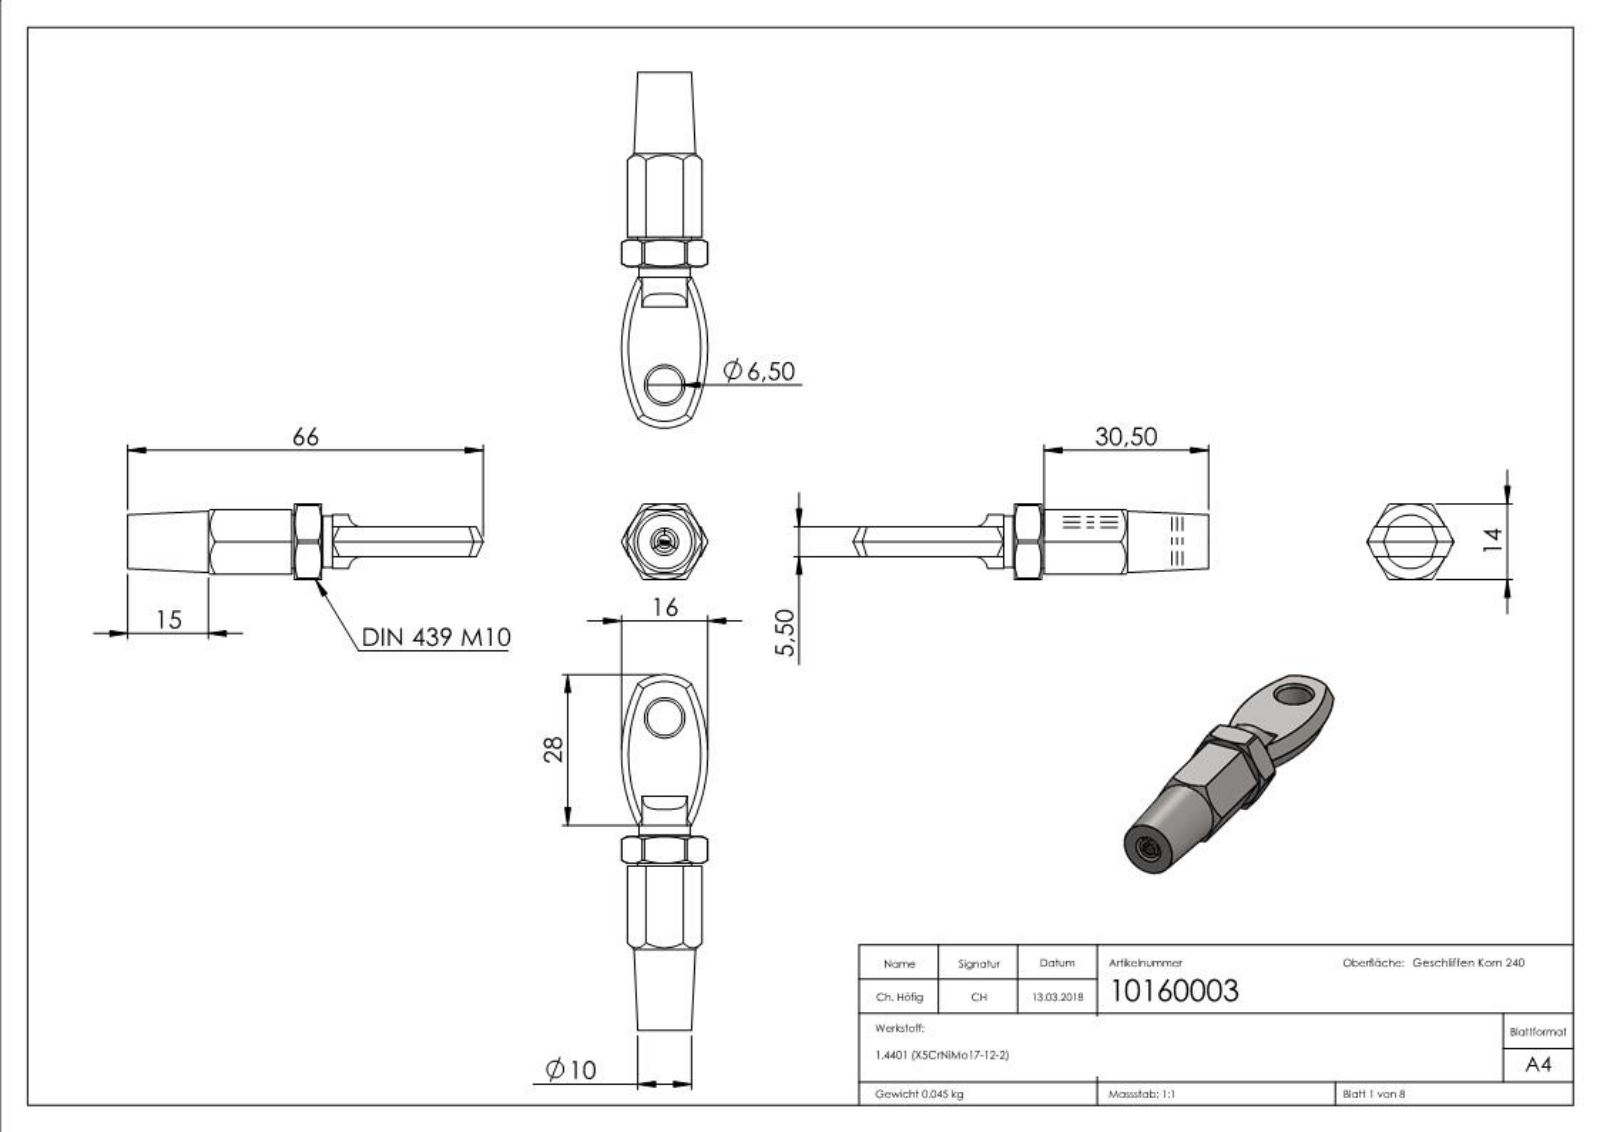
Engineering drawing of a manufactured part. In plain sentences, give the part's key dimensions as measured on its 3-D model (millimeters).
The part is named "1016000X Teil1_10160003 Teil1; 10160003; 1016000X Teil5_10160003 Teil5; 1016000X Teil3_10160003 Teil3 (+3 more)". Its 3-D file was written by "SolidWorks 2015 (CONFIG_CONTROL_DESIGN)". It is 8 solids with 494 faces: 135 planar, 107 cylindrical and 252 other. Overall it measures 66 by 16.01 by 14 millimeters. Its volume is 5 607 cubic millimeters and its surface area 4 995 square millimeters. Round holes: 1 of diameter 2.5, 1 of diameter 4, 1 of diameter 4.05, 1 of diameter 5.76, 1 of diameter 6.5, 1 of diameter 8.5. Round bosses or shafts: 1 of diameter 10, 1 of diameter 9.5, 1 of diameter 8. Partial cylindrical surfaces (rounded edges, fillets, slot ends): 6 of radius 0.5, 2 of radius 2.5, 2 of radius 28.72. The main face-to-face distances are 12, 5.5, 13, 1, 3.25, 8.75, 14, 15.25, 5, 4.25.
